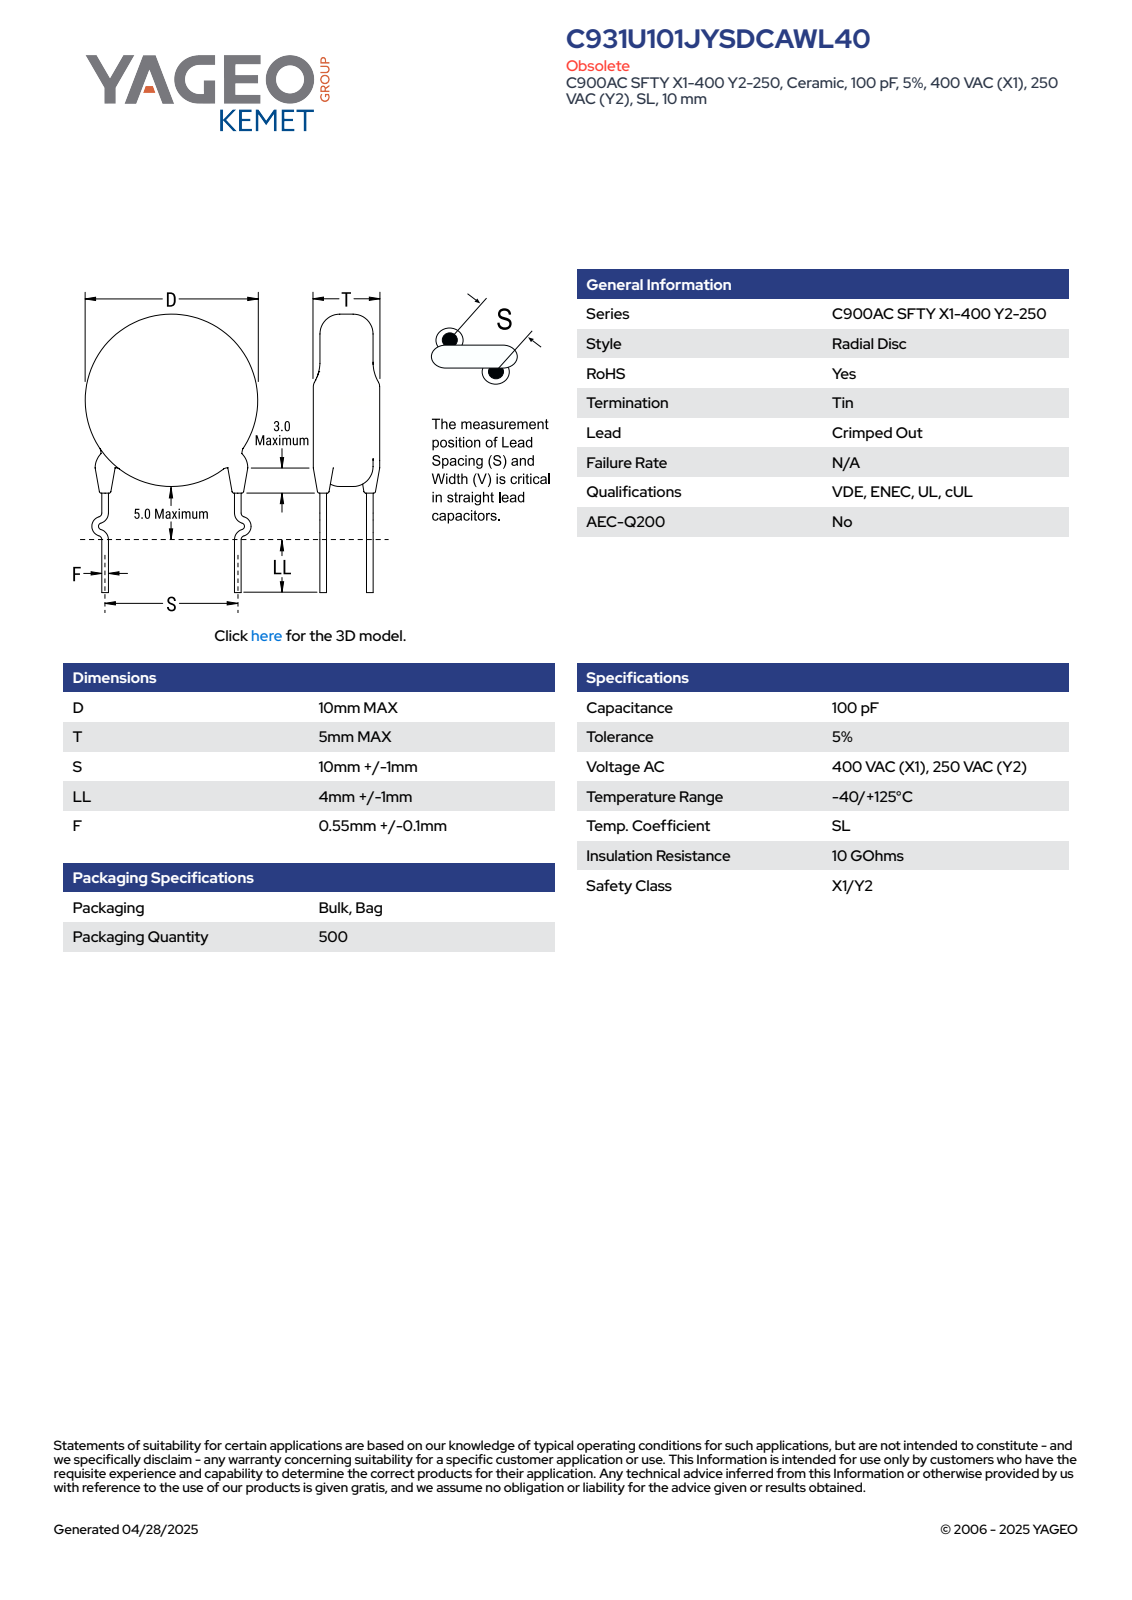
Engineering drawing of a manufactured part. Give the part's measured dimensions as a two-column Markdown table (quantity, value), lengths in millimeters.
| quantity | value |
| --- | --- |
| part name | CCD_KCOC900_D10T5S10LL5F0.55 |
| STEP written by | SolidWorks 2014 (AUTOMOTIVE_DESIGN) |
| units | millimeters |
| bodies | 4 solids, 87 faces (63 planar, 6 cylindrical, 18 other) |
| overall size | 20 × 14.7 × 5.45 |
| volume | 395 mm³ |
| surface area | 367 mm² |
| round bosses / shafts (diameter × count) | 1.2 × 2, 10 × 1 |
| main face-to-face distances | 5, 1.04, 5.53, 4.49, 0.84, 4.24, 0.38, 4.52, 3.08, 3.2 |
